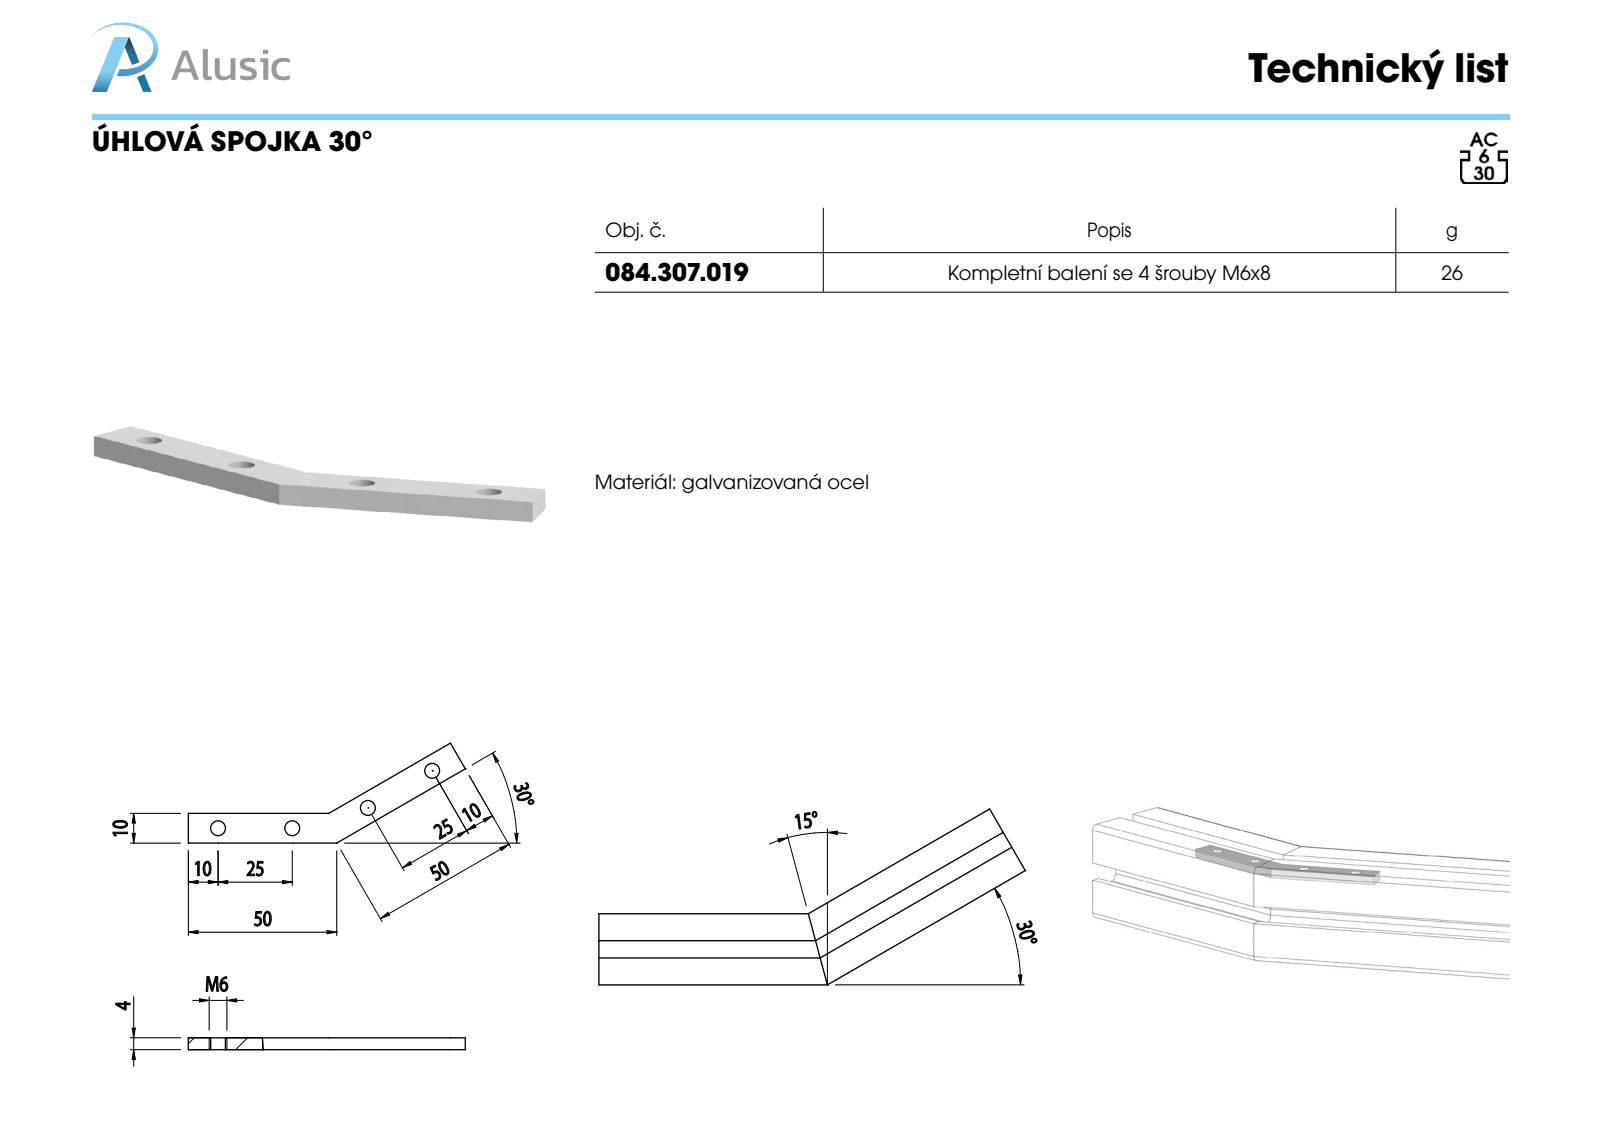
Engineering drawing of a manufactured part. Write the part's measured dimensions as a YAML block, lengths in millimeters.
part_name: "084.307.019"
step_written_by: "SolidWorks 2011 (CONFIG_CONTROL_DESIGN)"
units: millimeters
bodies: {solids: 1, faces: 16, planar: 8, cylindrical: 8, other: 0}
overall_size: [93.3, 33.66, 4]
volume: 3579
surface_area: 2899
round_holes:
  - {diameter: 5, count: 4}
face_to_face_distances: [4, 10]
hole_center_spacings: [25, 50.95, 26.39, 74.68]
